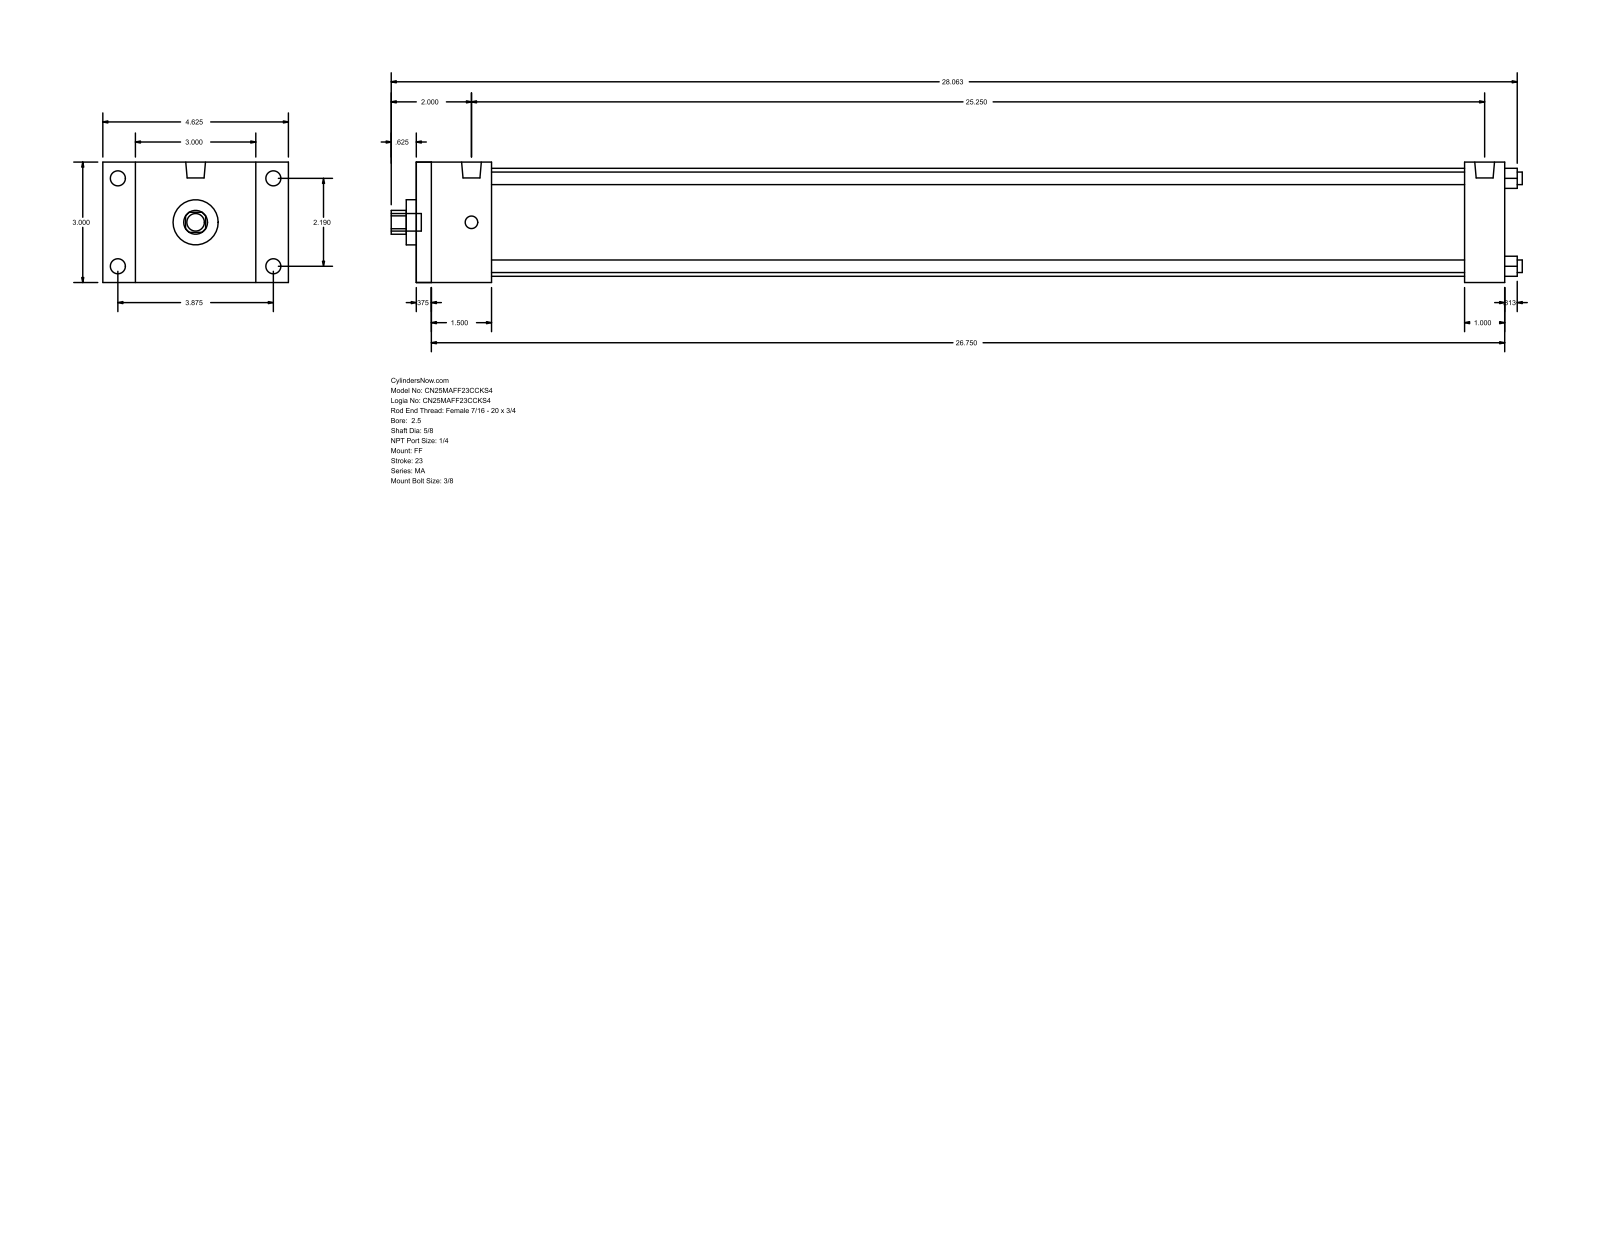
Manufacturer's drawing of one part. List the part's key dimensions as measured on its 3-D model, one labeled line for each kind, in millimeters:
Part name (STEP PRODUCT): MA_FF__0250_0.625
STEP written by: GSSL Pune (CONFIG_CONTROL_DESIGN)
Units: millimetres
Bodies: 0 solids, 92 faces (64 planar, 28 cylindrical, 0 other)
Overall size (bounding box): 715.96 × 117.47 × 76.2
Round holes (diameter × count): ⌀7.94 ×4, ⌀15.88 ×1, ⌀28.57 ×1, ⌀68.33 ×1
Round bosses / shafts (diameter × count): ⌀9.53 ×4, ⌀7.94 ×4, ⌀12.49 ×2, ⌀11.11 ×1
Partial cylindrical surfaces — rounded edges, fillets, slot ends (radius × count): R7.54 ×1
Main face-to-face distances: 76.2, 688.97, 9.52, 679.45, 25.4, 47.62, 663.57, 38.1, 654.05, 615.95
Hole centre spacings: 39.33, 55.62, 78.66
